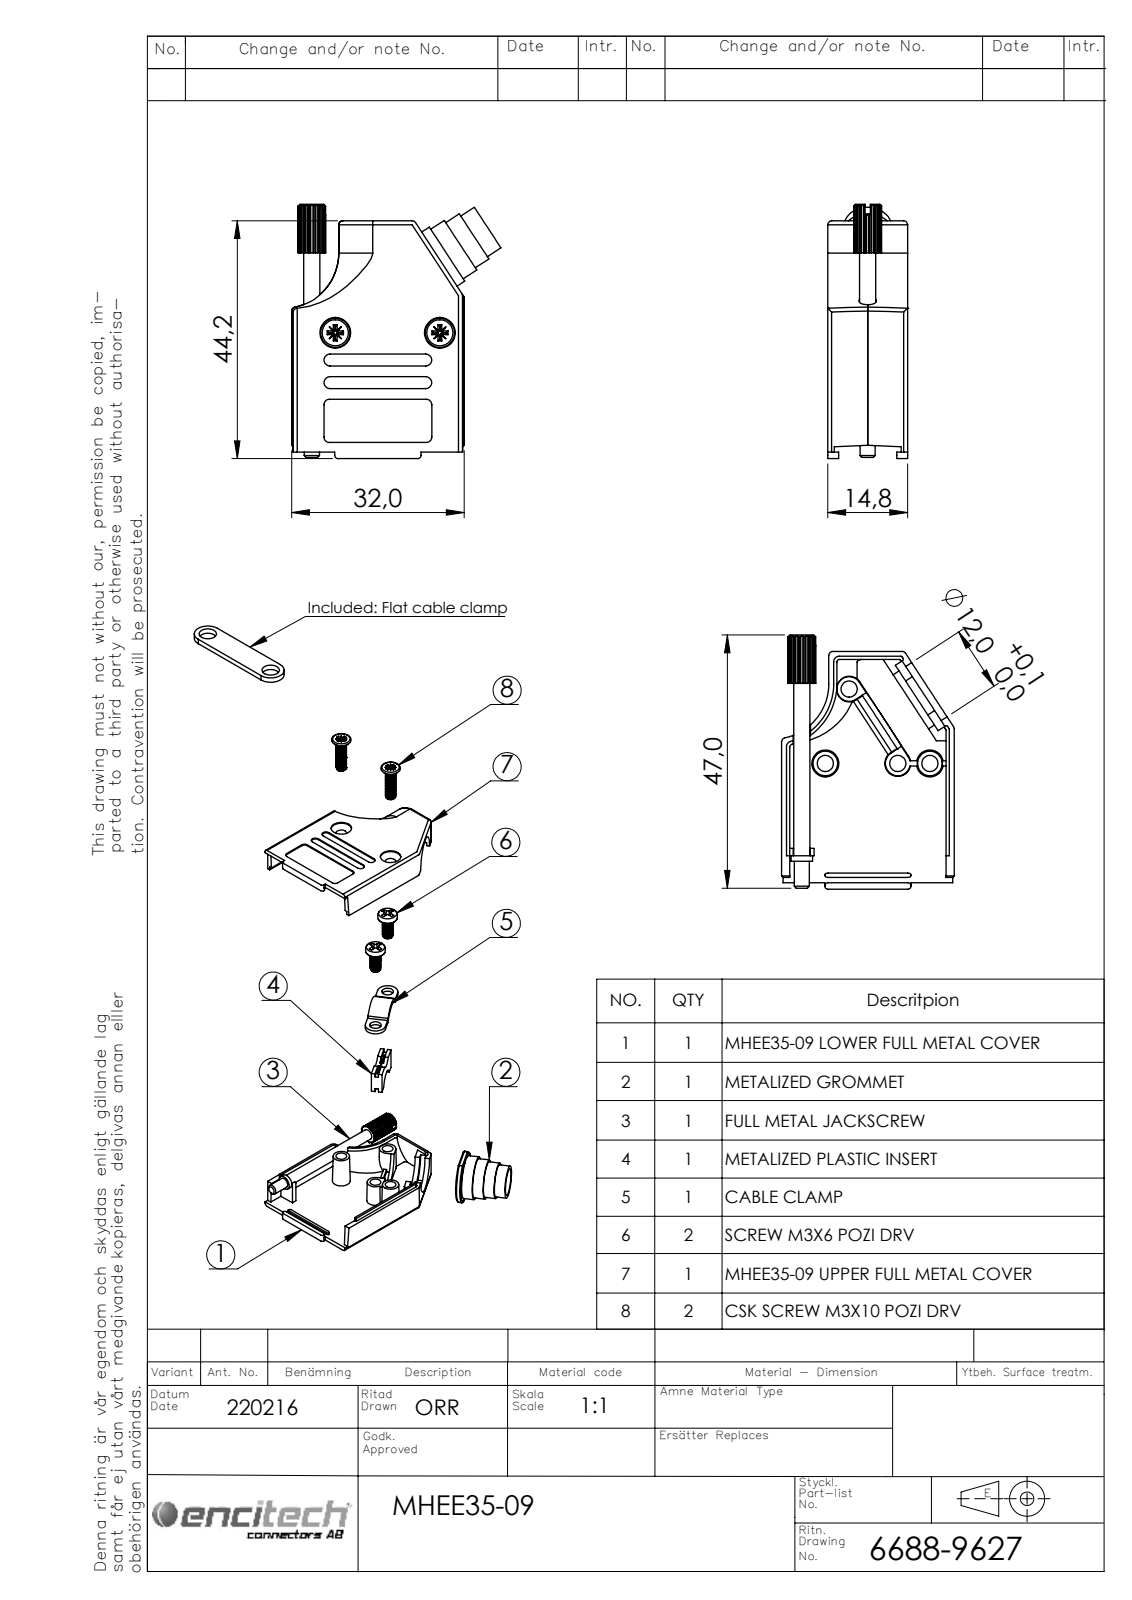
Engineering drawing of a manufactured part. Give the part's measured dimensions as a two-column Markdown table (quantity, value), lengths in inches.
| quantity | value |
| --- | --- |
| part name | 6805-0139-01; 6826-0141-02; 6560-0140-11; 6855-0117-13 (+5 more) |
| STEP written by | SolidWorks 2021 (AUTOMOTIVE_DESIGN) |
| units | inches |
| bodies | 10 solids, 740 faces (347 planar, 285 cylindrical, 108 other) |
| overall size | 1.858 × 1.528 × 0.583 |
| volume | 0.385 in³ |
| surface area | 18 in² |
| round holes (diameter × count) | 0.118 × 4, 0.126 × 3, 0.189 × 2, 0.224 × 2, 0.295 × 1, 0.335 × 1, 0.374 × 1, 0.413 × 1, 0.472 × 1 |
| round bosses / shafts (diameter × count) | 0.114 × 4, 0.433 × 1, 0.394 × 1, 0.354 × 1, 0.228 × 1, 0.157 × 1, 0.118 × 1, 0.11 × 1 |
| partial cylindrical surfaces (radius × count) | 0.03 × 11, 0.004 × 8, 0.039 × 8, 0.012 × 7, 0.043 × 4, 0.02 × 2, 0.024 × 2, 0.112 × 2 |
| main face-to-face distances | 0.047, 0.535, 0.488, 0.583, 0.035, 0.571, 0.524, 0.244, 0.291, 1.258 |
| hole center spacings | 0.235, 0.529, 0.571, 0.649, 0.764, 0.802 |
